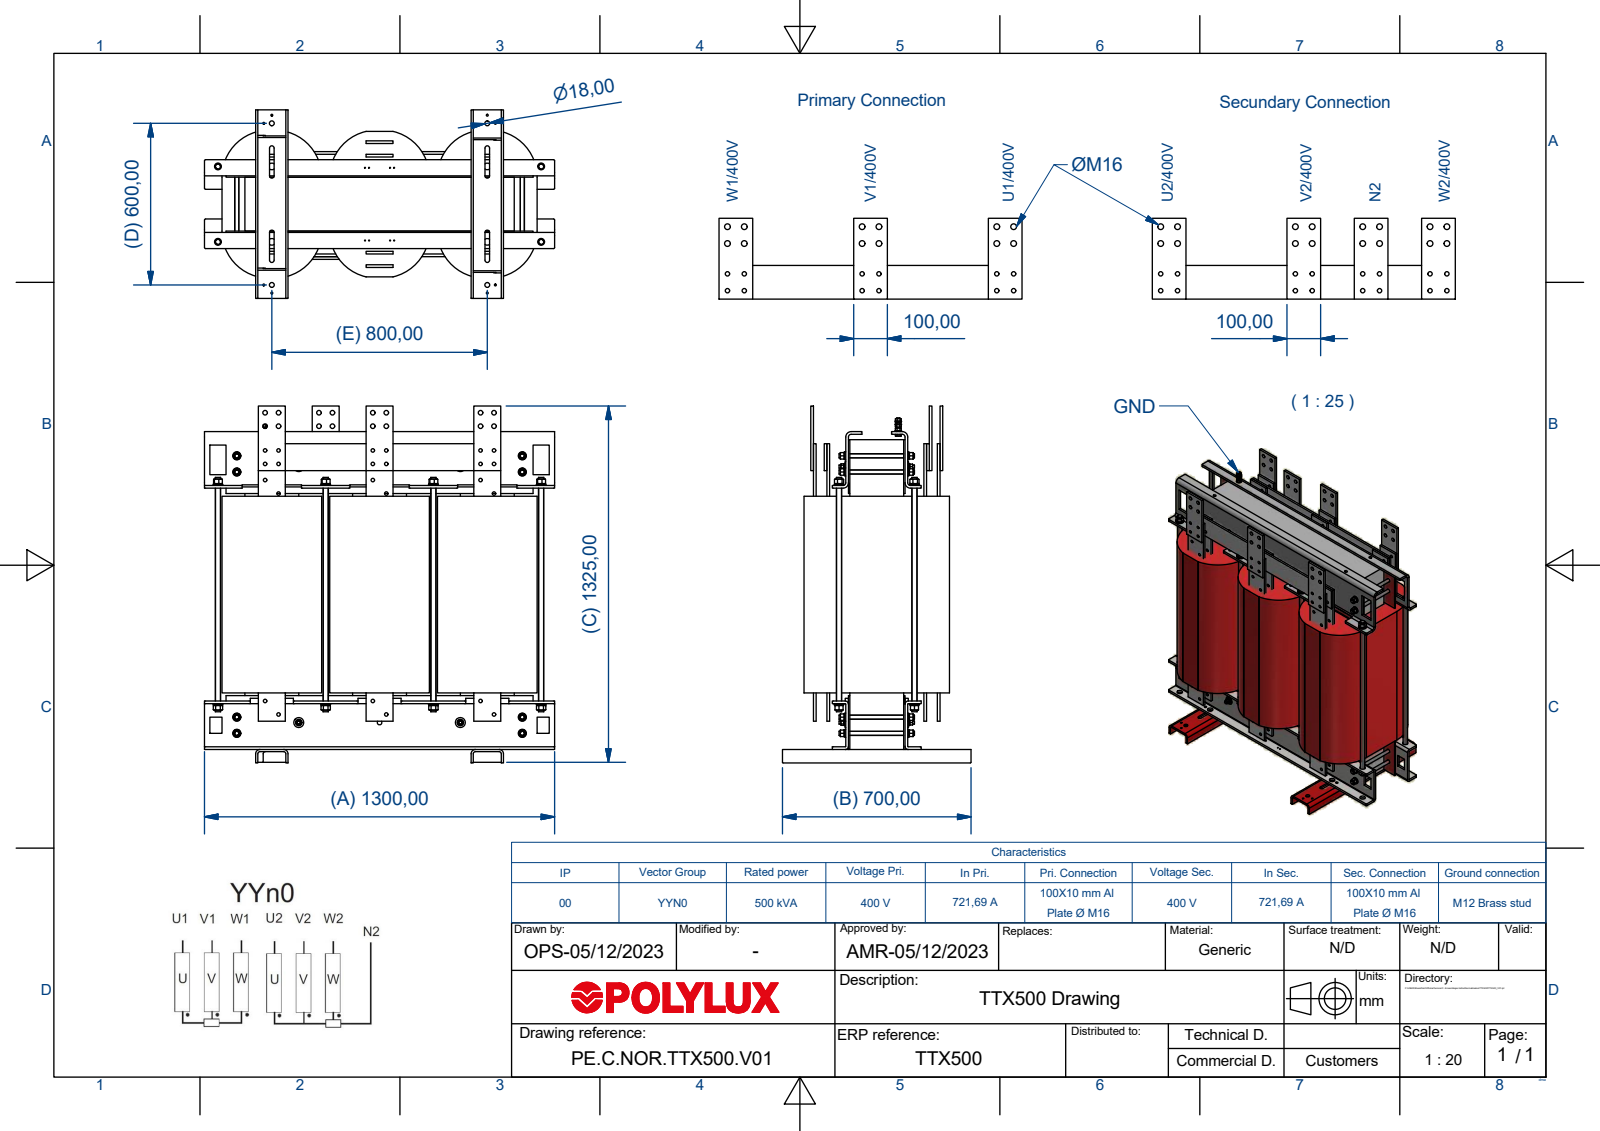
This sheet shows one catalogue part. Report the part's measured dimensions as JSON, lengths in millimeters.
{"part_name": "TTX500_V01", "step_written_by": "Autodesk Inventor 2018 (AUTOMOTIVE_DESIGN)", "units": "millimeters", "bodies": {"solids": 195, "faces": 2038, "planar": 1118, "cylindrical": 660, "other": 260}, "overall_size": [1325, 1300, 700], "volume_mm3": 506900000, "surface_area_mm2": 19070000, "round_holes": [[13, 48], [17, 30], [11, 24], [25, 12], [15, 10], [3.5, 8], [7, 8], [13.84, 8], [17.29, 8], [21, 8], [21.2, 8], [22, 6]], "round_bosses_or_shafts": [[37, 12], [33.6, 8], [30, 8], [27.4, 8], [20, 8], [16, 8], [24, 5], [21.1, 5]], "partial_cylinders_radius": [[4, 32], [10, 16], [174.54, 12], [8.5, 8], [8, 6], [2, 4], [12, 4], [16, 4]], "face_to_face_distances": [200, 10, 400, 85, 50, 5, 205, 285, 70, 210], "hole_center_spacings": [400, 300, 100, 600, 200, 800, 488.26, 30]}
